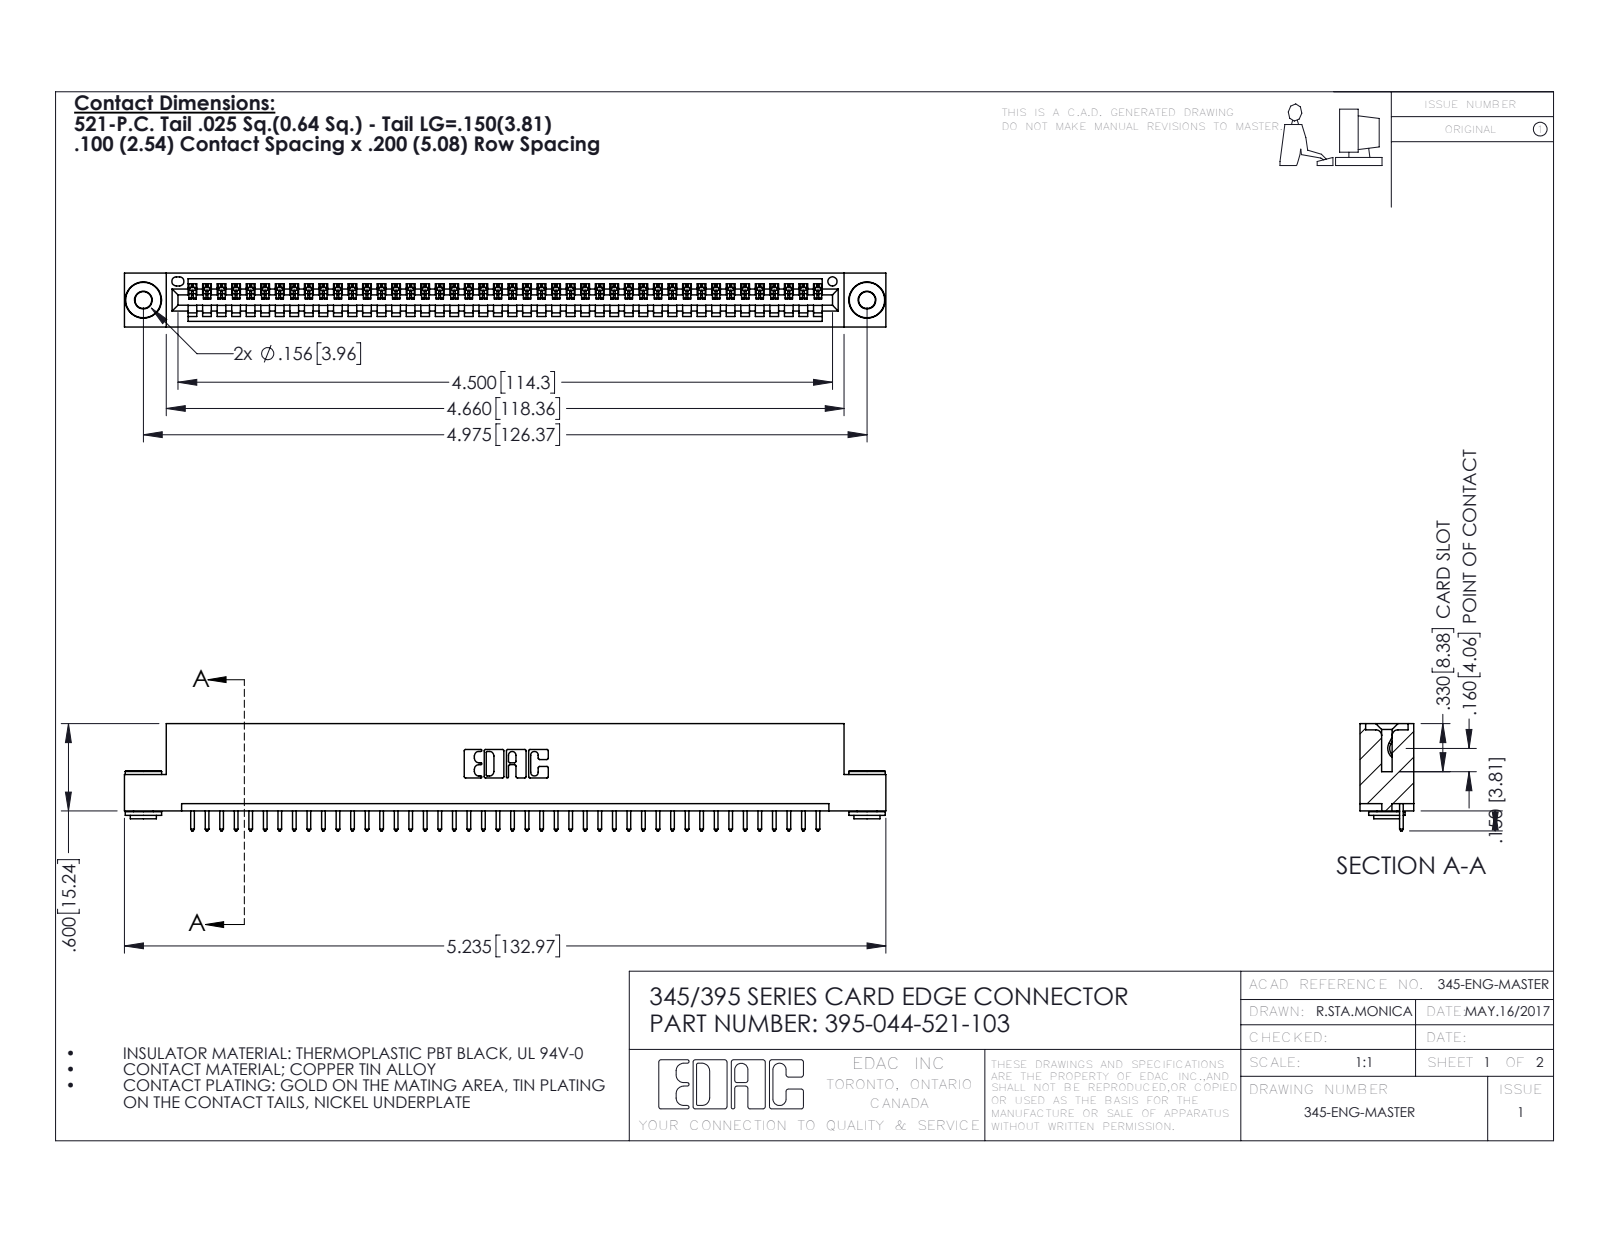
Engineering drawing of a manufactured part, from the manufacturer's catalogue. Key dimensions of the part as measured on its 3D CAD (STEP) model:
Part name (STEP PRODUCT): 395-044-521-103; 345-292-001_345-293-121; 345 Part_Flush Mounting Lugs - 0.156 Dia-TH; 345-250-002_345-250-002-102
STEP written by: SolidWorks 2016 (CONFIG_CONTROL_DESIGN)
Units: inches
Bodies: 47 solids, 2716 faces (1850 planar, 858 cylindrical, 8 other)
Overall size (bounding box): 5.235 × 0.737 × 0.37
Volume: 0.765 in³ · Surface area: 25.45 in²
Round holes (diameter × count): ⌀0.116 ×2, ⌀0.156 ×2, ⌀0.064 ×1
Round bosses / shafts (diameter × count): ⌀0.25 ×2, ⌀0.18 ×2, ⌀0.136 ×2
Partial cylindrical surfaces — rounded edges, fillets, slot ends (radius × count): R0.006 ×88, R0.01 ×88, R0.01 ×22, R0.007 ×6, R0.031 ×6, R0.026 ×3, R0.031 ×2, R0.04 ×2
Main face-to-face distances: 0.072, 0.298, 0.37, 0.2, 0.025, 0.098, 0.272, 0.225, 0.149, 0.072
Hole centre spacings: 0.27, 4.739, 4.975
